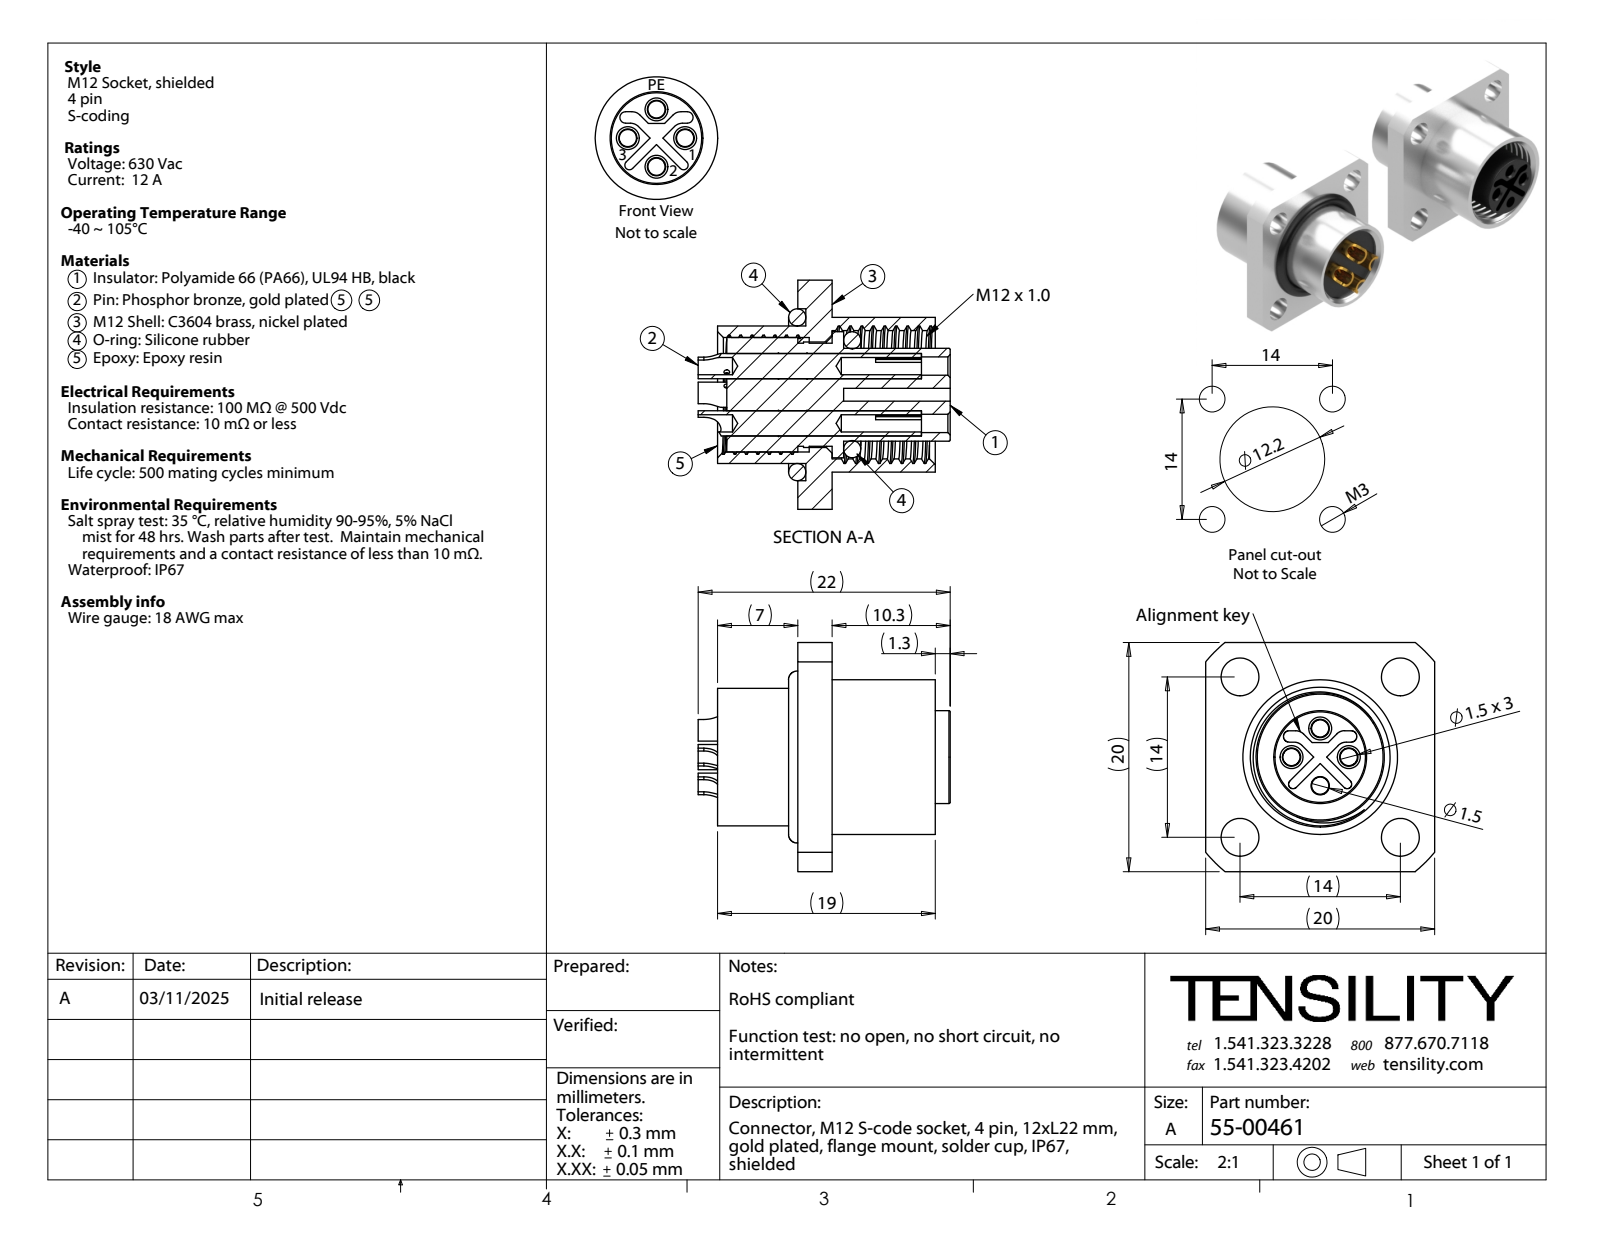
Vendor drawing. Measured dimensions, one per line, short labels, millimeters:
name: 55-00461-03; 55-00461-02; 55-00461-01; 55-00461-04 (+2 more)
written by: SolidWorks 2021 (CONFIG_CONTROL_DESIGN)
unit: mm
bodies: 8 solids, 293 faces (89 planar, 141 cylindrical, 63 other)
size: 22 × 20 × 20
volume: 2 629 mm³; area: 5 050 mm²
holes: 4× ⌀1.5, 4× ⌀1.6, 4× ⌀3.3, 2× ⌀0.5, 1× ⌀9, 1× ⌀9.2, 1× ⌀10, 1× ⌀11.2, 1× ⌀15
bosses: 4× ⌀2.2, 1× ⌀13.5, 1× ⌀12, 1× ⌀11, 1× ⌀8.1
rounds: 4× R1, 2× R0.4, 2× R0.5, 2× R1.86, 1× R13
face distances: 3, 20, 0.8, 1, 9.2, 0.7, 2.3, 6.2, 6.9, 4
hole spacings: 8.32, 11.8, 3.54, 2.5, 9.9, 14, 5, 19.8
